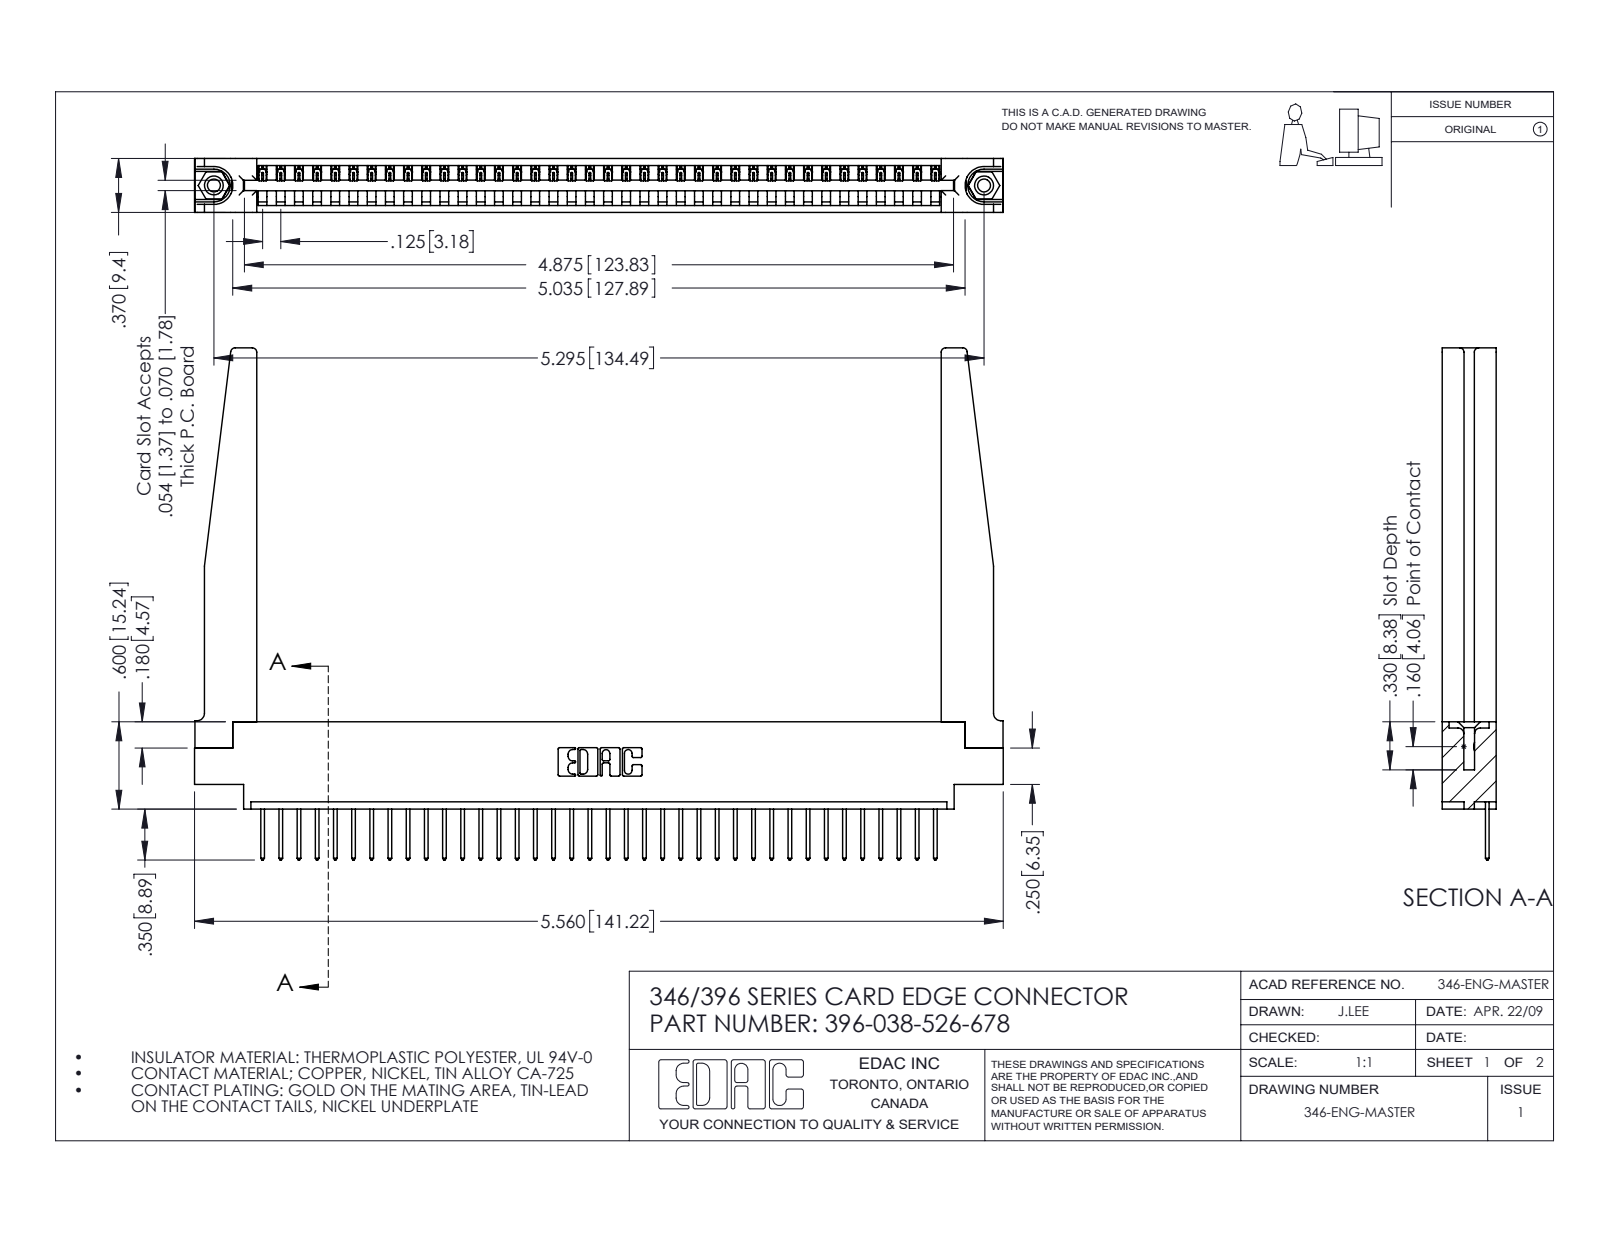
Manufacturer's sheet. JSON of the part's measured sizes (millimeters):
{"part_name": "396-038-526-678; 346-220-078_345-220-078; 345-292-001_345-293-126; 346 Part_0.170 Offset - 0.156 Dia-TH (+1 more)", "step_written_by": "SolidWorks 2016 (CONFIG_CONTROL_DESIGN)", "units": "millimeters", "bodies": {"solids": 43, "faces": 2564, "planar": 1742, "cylindrical": 770, "other": 52}, "overall_size": [141.2, 89.4, 9.4], "volume_mm3": 20220, "surface_area_mm2": 23250, "round_holes": [[2.3, 2], [3.2, 2], [4, 2], [1.6, 1]], "round_bosses_or_shafts": [[3.9, 2]], "partial_cylinders_radius": [[0.2, 76], [0.3, 76], [0.3, 22], [0.8, 8], [0.2, 6], [0.8, 6], [0.7, 3], [0.8, 2]], "face_to_face_distances": [9.4, 1.2, 8.2, 1.8, 3.8, 6.4, 3.8, 7.6, 0.6, 5.6], "hole_center_spacings": [6.2, 129.2, 134.5]}
